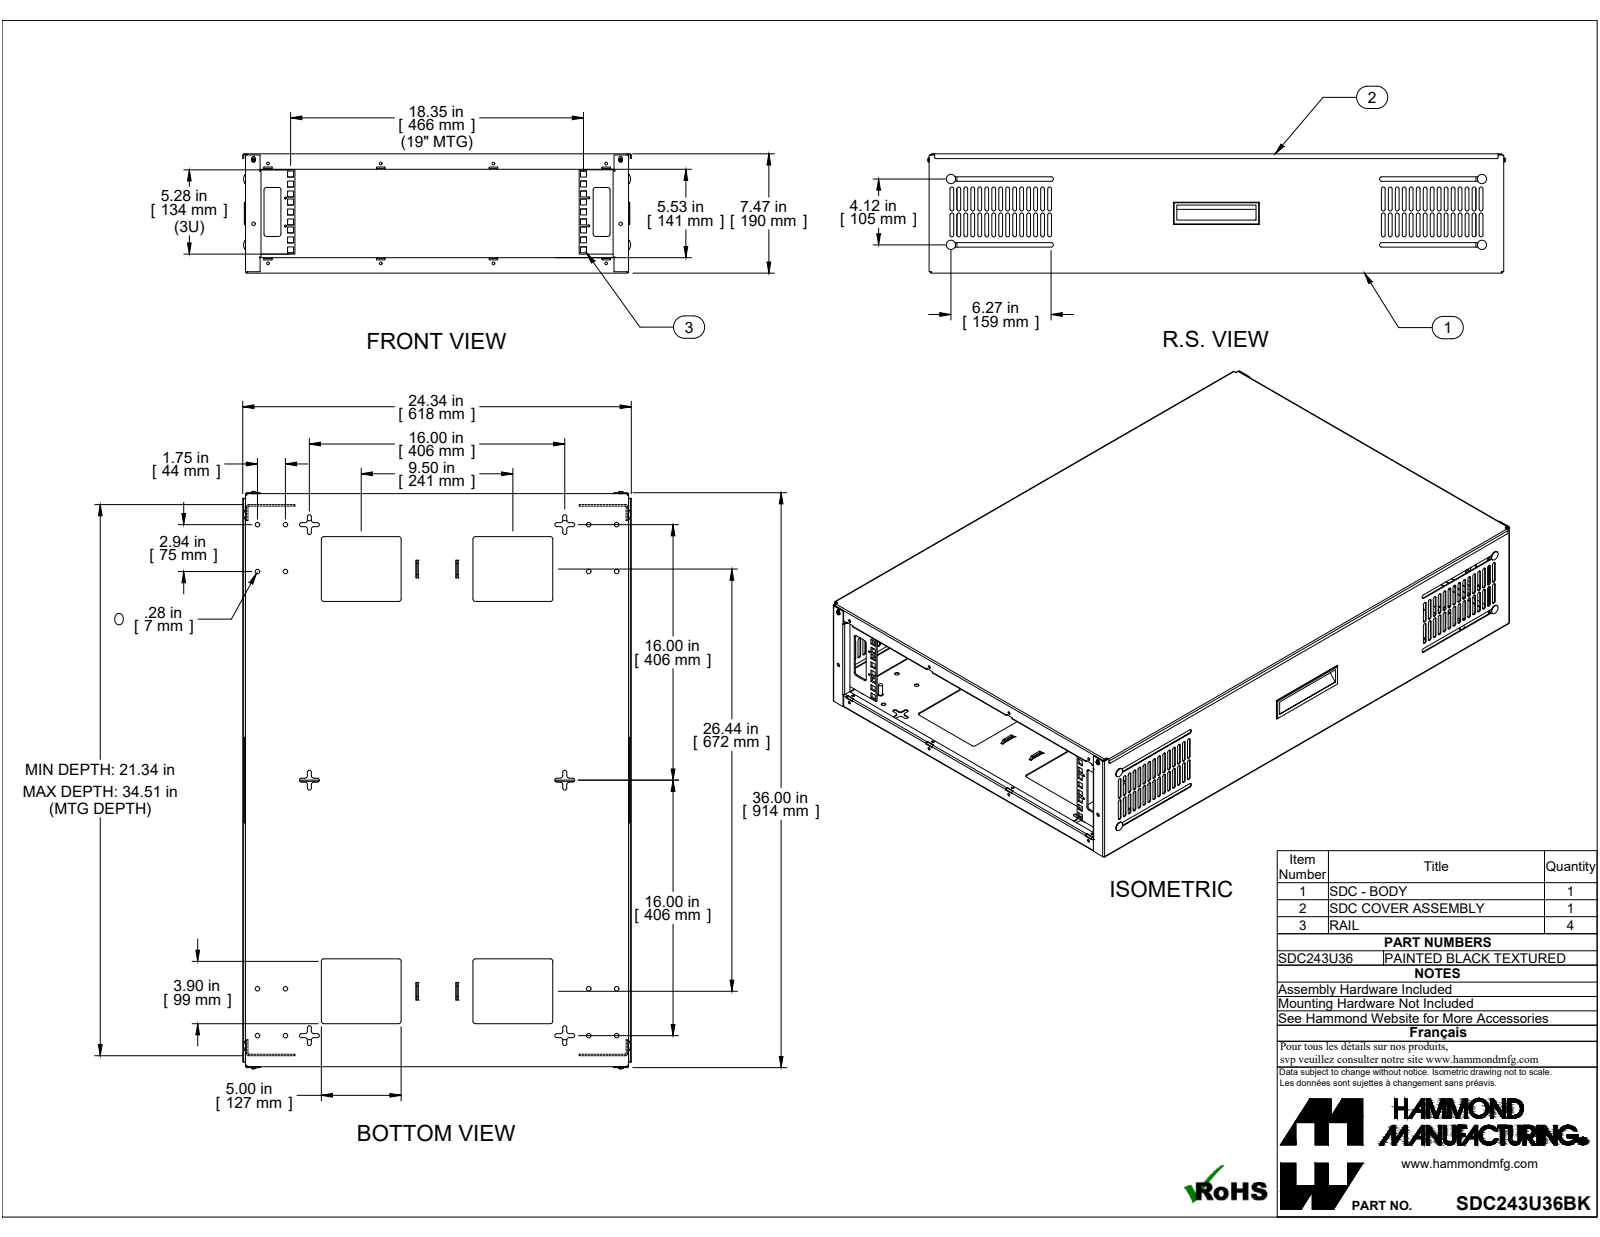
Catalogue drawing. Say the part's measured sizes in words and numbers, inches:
The part is named "SDC243U36BK". Its 3-D file was written by "SolidWorks 2019 (CONFIG_CONTROL_DESIGN)". It is 37 solids with 1932 faces: 1222 planar, 658 cylindrical and 52 other. Overall it measures 36.17 by 24.344 by 7.472 inches. Its volume is 147.4 cubic inches and its surface area 5 071 square inches. Round holes: 16 of diameter 0.17, 16 of diameter 0.281, 8 of diameter 0.125, 4 of diameter 0.196, 2 of diameter 0.159, 2 of diameter 0.187, 2 of diameter 0.213. Round bosses or shafts: 8 of diameter 0.25, 4 of diameter 0.58, 2 of diameter 0.313, 2 of diameter 0.28, 2 of diameter 0.187, 2 of diameter 0.138. Partial cylindrical surfaces (rounded edges, fillets, slot ends): 120 of radius 0.118, 52 of radius 0.157, 24 of radius 0.125, 22 of radius 0.029, 22 of radius 0.086, 16 of radius 0.025, 16 of radius 0.117, 8 of radius 0.03. The main face-to-face distances are 0.057, 7.415, 7.358, 7.472, 23.943, 23.886, 24, 0.072, 7.343, 0.129. The hole center spacings are 1.75, 2.937, 3.419, 7.063, 19.005, 19.085, 20.75, 20.957.
